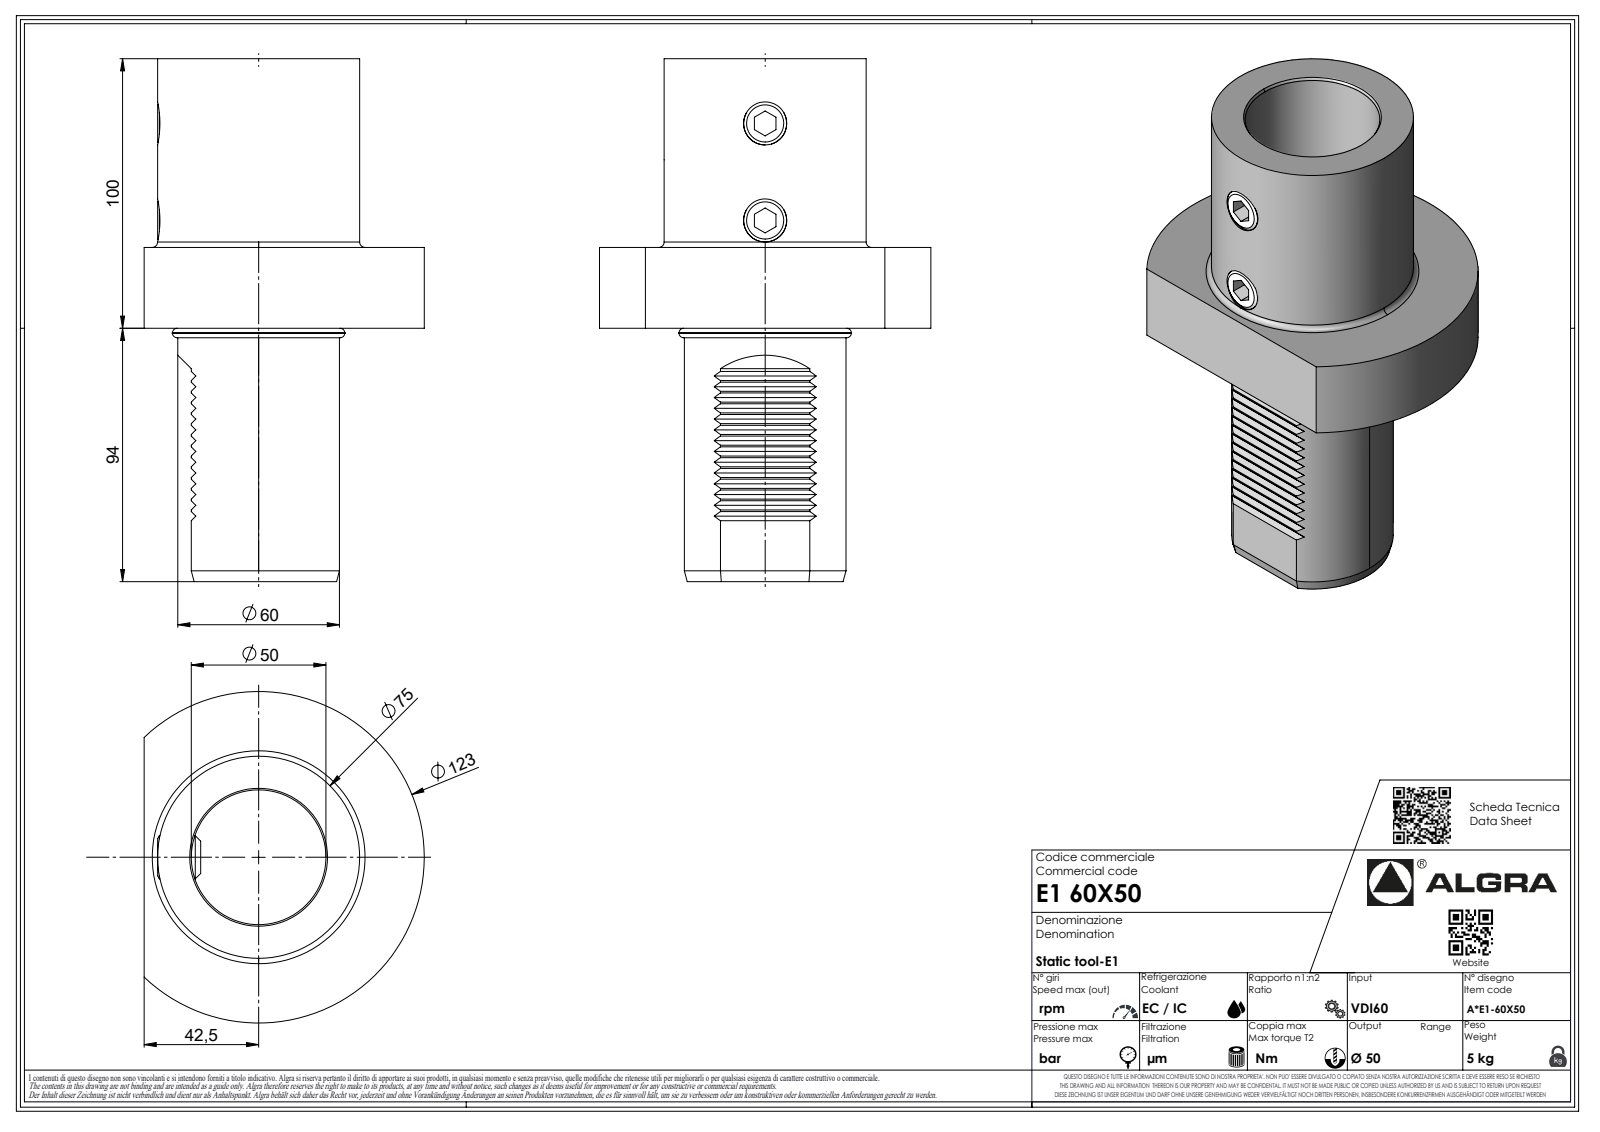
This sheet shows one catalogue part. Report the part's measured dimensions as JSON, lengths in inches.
{"part_name": "E160X50", "step_written_by": "SolidWorks 2023 (AUTOMOTIVE_DESIGN)", "units": "inches", "bodies": {"solids": 1, "faces": 285, "planar": 194, "cylindrical": 42, "other": 49}, "overall_size": [7.638, 4.843, 4.094], "volume_in3": 44.13, "surface_area_in2": 125.6, "round_holes": [[0.083, 1], [1.969, 1]], "round_bosses_or_shafts": [[0.63, 2], [2.953, 1], [2.527, 1], [2.362, 1], [0.251, 1], [0.067, 1]], "partial_cylinders_radius": [[0.013, 7], [0.02, 7], [0.146, 7], [0.008, 1], [2.421, 1]], "face_to_face_distances": [1.181, 4.882, 3.701, 2.756, 3.937, 7.638, 0.63, 3.307, 0.551, 4.331]}
